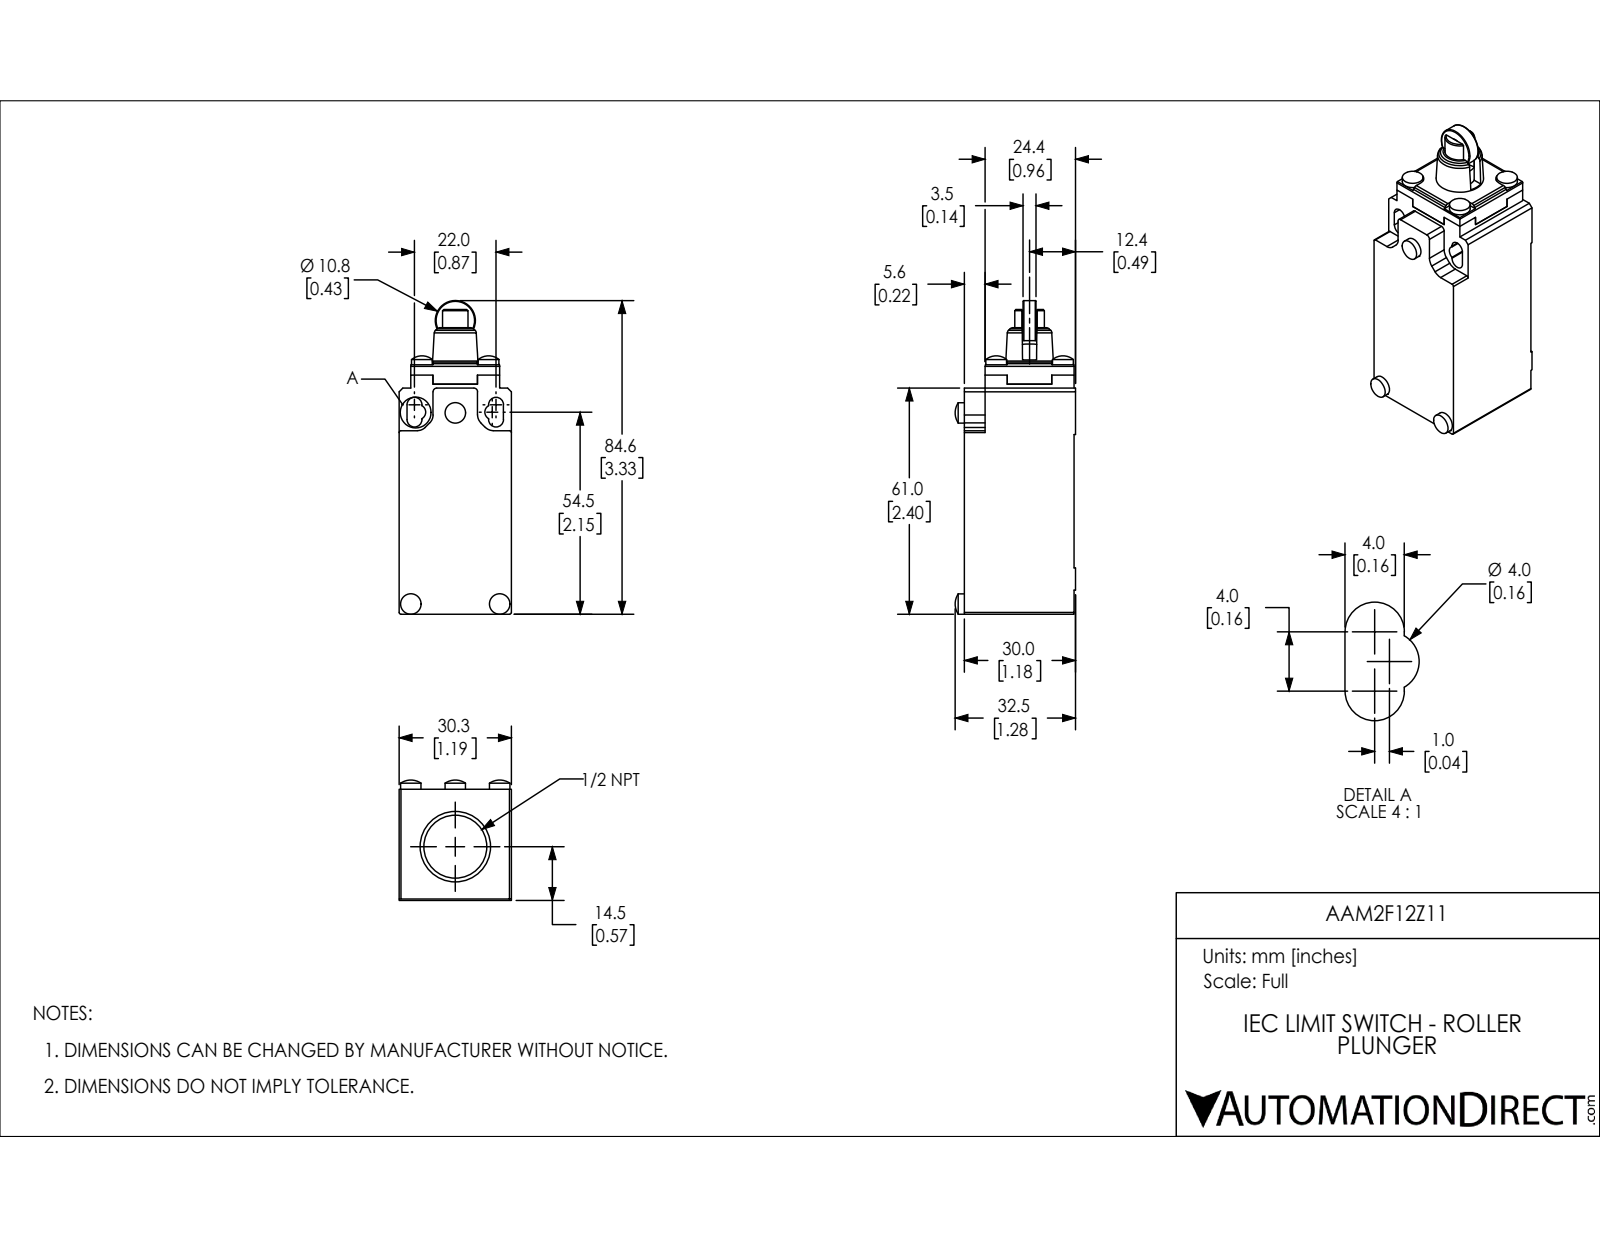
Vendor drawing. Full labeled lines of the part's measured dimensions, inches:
Part name (STEP PRODUCT): AAM2F12Z11
STEP written by: SolidWorks 2018 (AUTOMOTIVE_DESIGN)
Units: inches
Bodies: 4 solids, 208 faces (96 planar, 85 cylindrical, 27 other)
Overall size (bounding box): 3.331 × 1.28 × 1.193
Volume: 3.438 in³ · Surface area: 21.71 in²
Round holes (diameter × count): ⌀0.319 ×1, ⌀0.669 ×1, ⌀0.748 ×1
Round bosses / shafts (diameter × count): ⌀0.22 ×5, ⌀0.217 ×3, ⌀0.425 ×1, ⌀0.315 ×1
Partial cylindrical surfaces — rounded edges, fillets, slot ends (radius × count): R0.039 ×10, R0.118 ×8, R0.079 ×6, R0.02 ×4, R0.394 ×1, R0.4 ×1, R0.787 ×1
Main face-to-face distances: 1.193, 1.165, 0.016, 1.181, 0.236, 2.444, 0.945, 2.445, 0.15, 0.124
Hole centre spacings: 0.083
